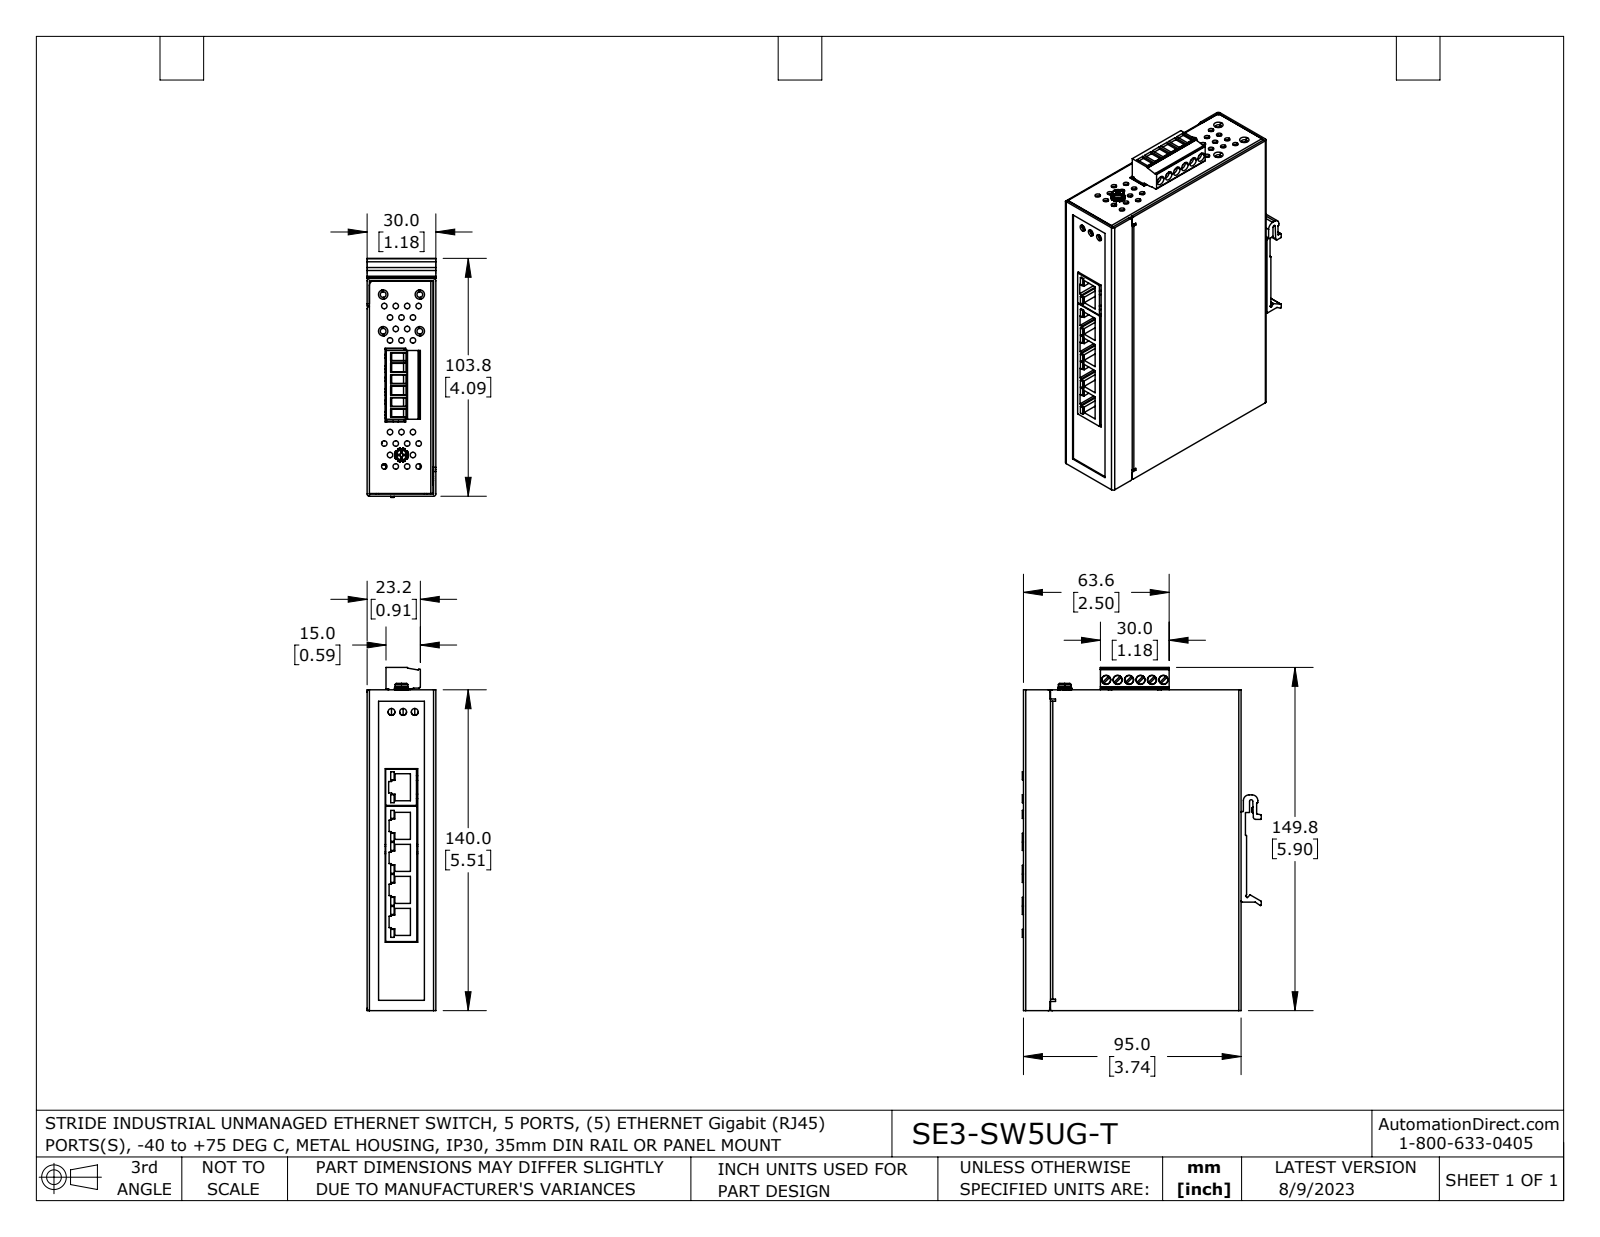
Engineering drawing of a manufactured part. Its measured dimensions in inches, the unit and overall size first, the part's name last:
Units: inches
Overall size (bounding box): 5.896 × 4.106 × 1.181
Round holes (diameter × count): ⌀0.094 ×51, ⌀0.098 ×14, ⌀0.157 ×9, ⌀0.118 ×3, ⌀0.138 ×2, ⌀0.059 ×1
Round bosses / shafts (diameter × count): ⌀0.161 ×10, ⌀0.149 ×6, ⌀0.02 ×6, ⌀0.197 ×5, ⌀0.118 ×5, ⌀0.11 ×5, ⌀0.213 ×4, ⌀0.217 ×1
Partial cylindrical surfaces — rounded edges, fillets, slot ends (radius × count): R0.004 ×77, R0.008 ×29, R0.039 ×27, R0.01 ×20, R0.02 ×13, R0.008 ×10, R0.079 ×9, R0.034 ×6
Main face-to-face distances: 0.039, 1.142, 0.02, 1.102, 1.181, 0.059, 1.122, 5.472, 3.681, 3.701
Hole centre spacings: 0.22, 0.394, 0.197, 0.44, 0.355, 2.168, 0.599, 1.774
Volume: 4.25 in³ · Surface area: 161.9 in²
Bodies: 14 solids, 1806 faces (845 planar, 721 cylindrical, 240 other)
Part name (STEP PRODUCT): LEONTON_EG2-0500_3D sr1 solid but 19 bad faces1 extTB1a coord fxt sr1
STEP written by: SolidWorks 2021 (AUTOMOTIVE_DESIGN)
